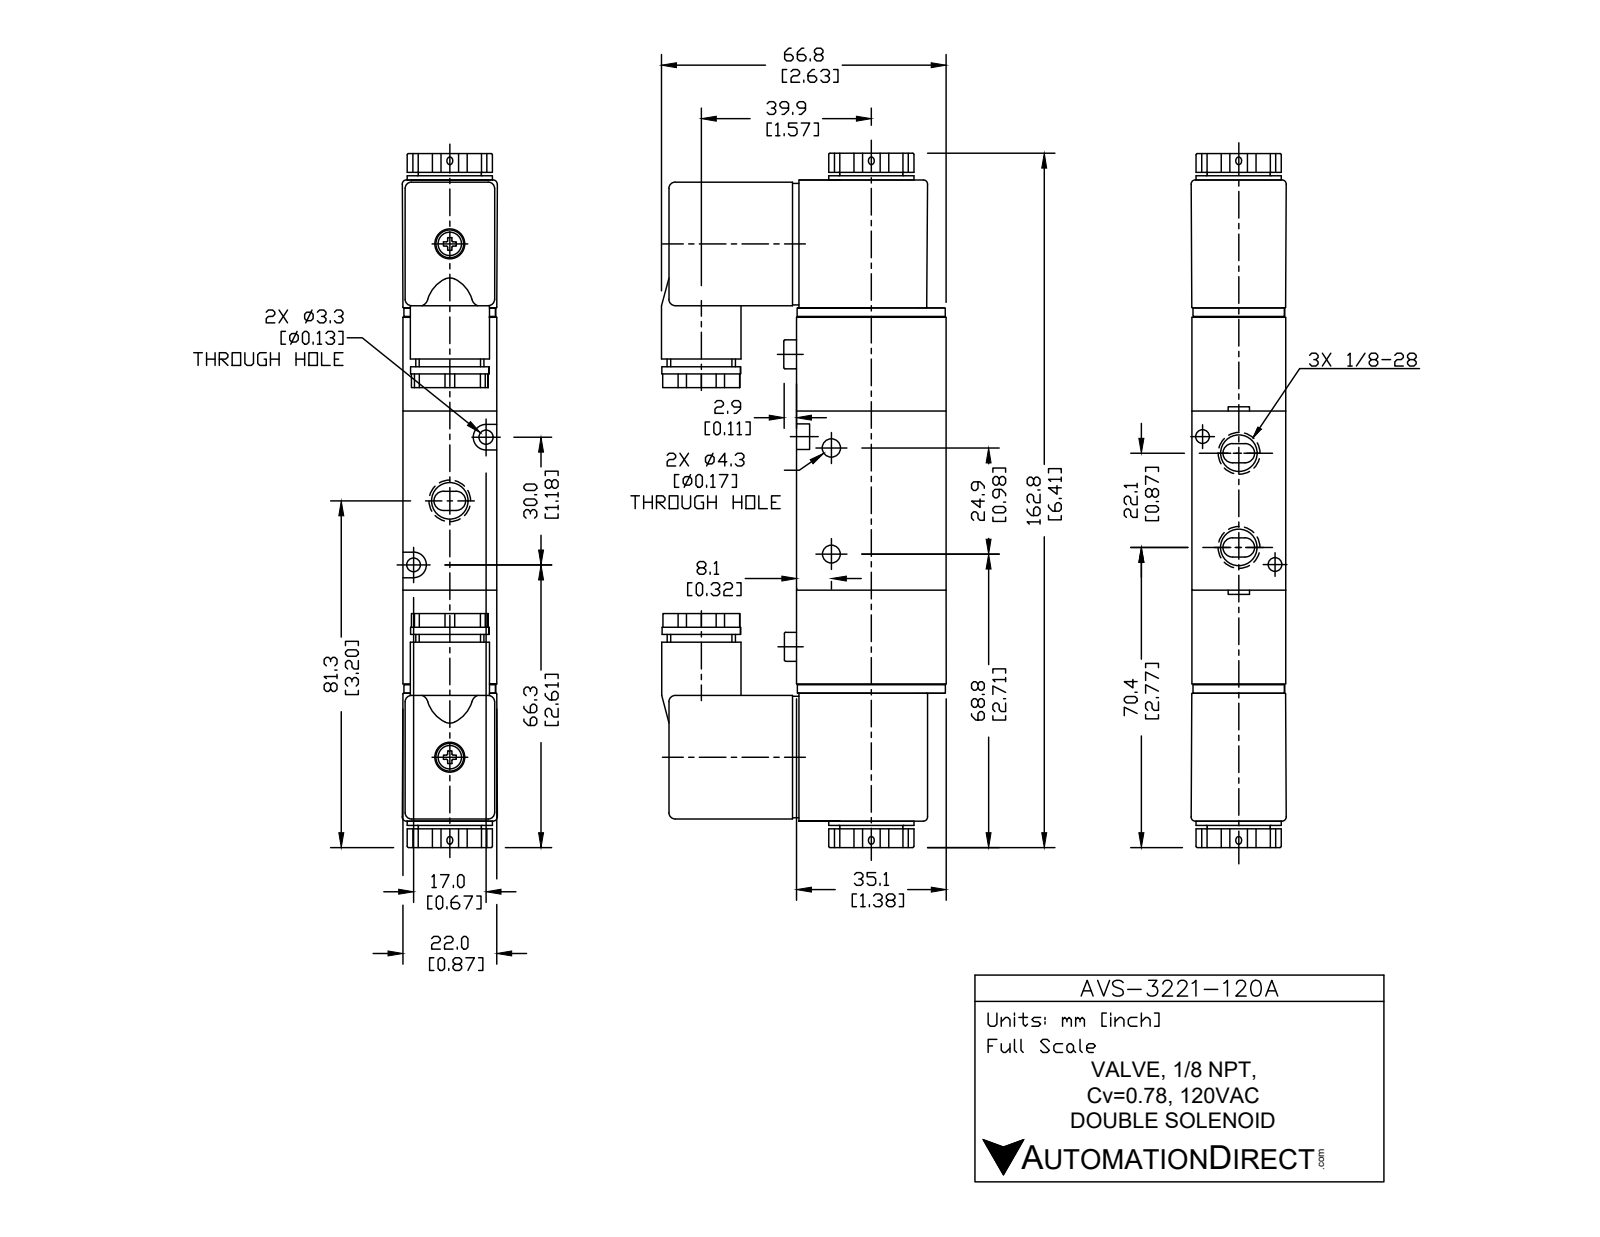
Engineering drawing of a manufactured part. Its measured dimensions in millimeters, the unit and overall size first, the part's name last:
Units: millimetres
Overall size (bounding box): 162.8 × 66.7 × 22
Round holes (diameter × count): ⌀8.43 ×3, ⌀3.3 ×2, ⌀4.3 ×2, ⌀9.3 ×1
Round bosses / shafts (diameter × count): ⌀6.8 ×2, ⌀20 ×1, ⌀18.6 ×1, ⌀18.4 ×1, ⌀16 ×1, ⌀14.8 ×1
Partial cylindrical surfaces — rounded edges, fillets, slot ends (radius × count): R1 ×20, R0.5 ×12, R3 ×2
Main face-to-face distances: 0.5, 22.6, 21.5, 21, 42, 22.82, 22.38, 22, 53.7, 95.7
Hole centre spacings: 17.24, 9.35, 9.39, 11, 11.1, 22.1, 25, 27.35
Volume: 153 516 mm³ · Surface area: 33 903 mm²
Bodies: 5 solids, 252 faces (138 planar, 82 cylindrical, 32 other)
Part name (STEP PRODUCT): AVS-3221-120A
STEP written by: SolidWorks 2015 (CONFIG_CONTROL_DESIGN)
